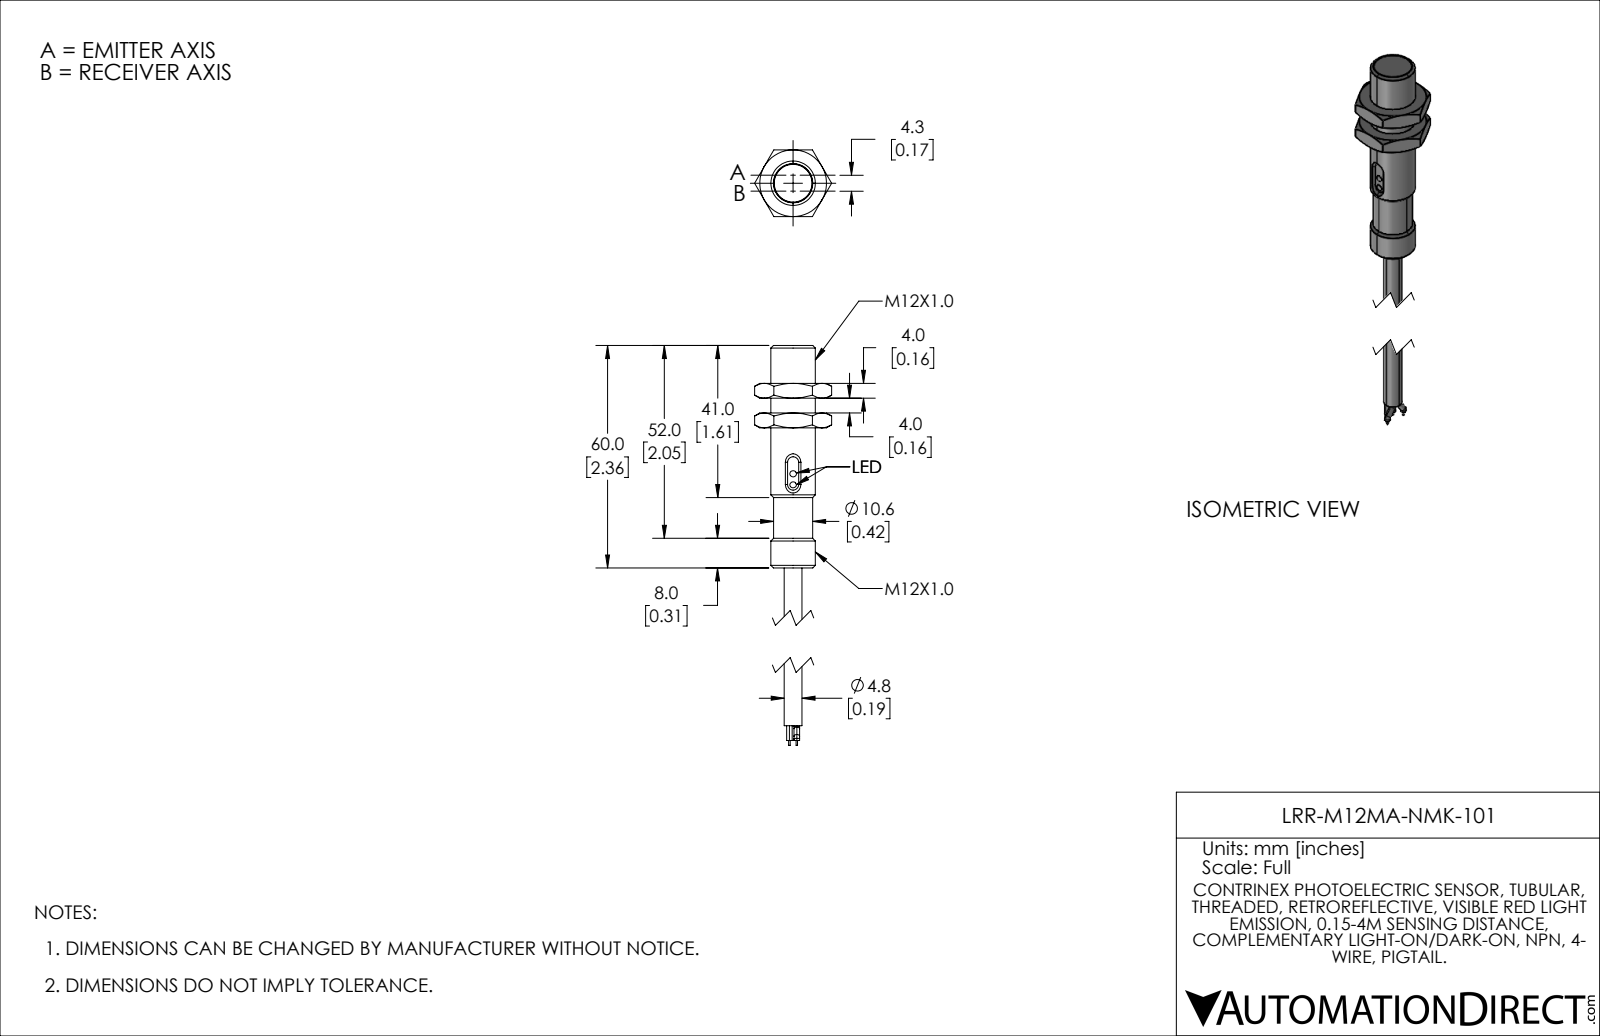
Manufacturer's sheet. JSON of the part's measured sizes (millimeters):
{"part_name": "LRR-M12MA-NMK-101", "step_written_by": "SolidWorks 2021 (AUTOMOTIVE_DESIGN)", "units": "millimeters", "bodies": {"solids": 3, "faces": 141, "planar": 31, "cylindrical": 44, "other": 66}, "overall_size": [145.3, 20.8, 18], "volume_mm3": 10200, "surface_area_mm2": 5551, "round_holes": [[10.2, 1]], "round_bosses_or_shafts": [[1.5, 6], [0.4, 4], [12, 1], [10.5, 1], [4.8, 1]], "face_to_face_distances": [10, 18, 6, 16, 4, 20, 26, 59.8, 49.8, 43.8]}
